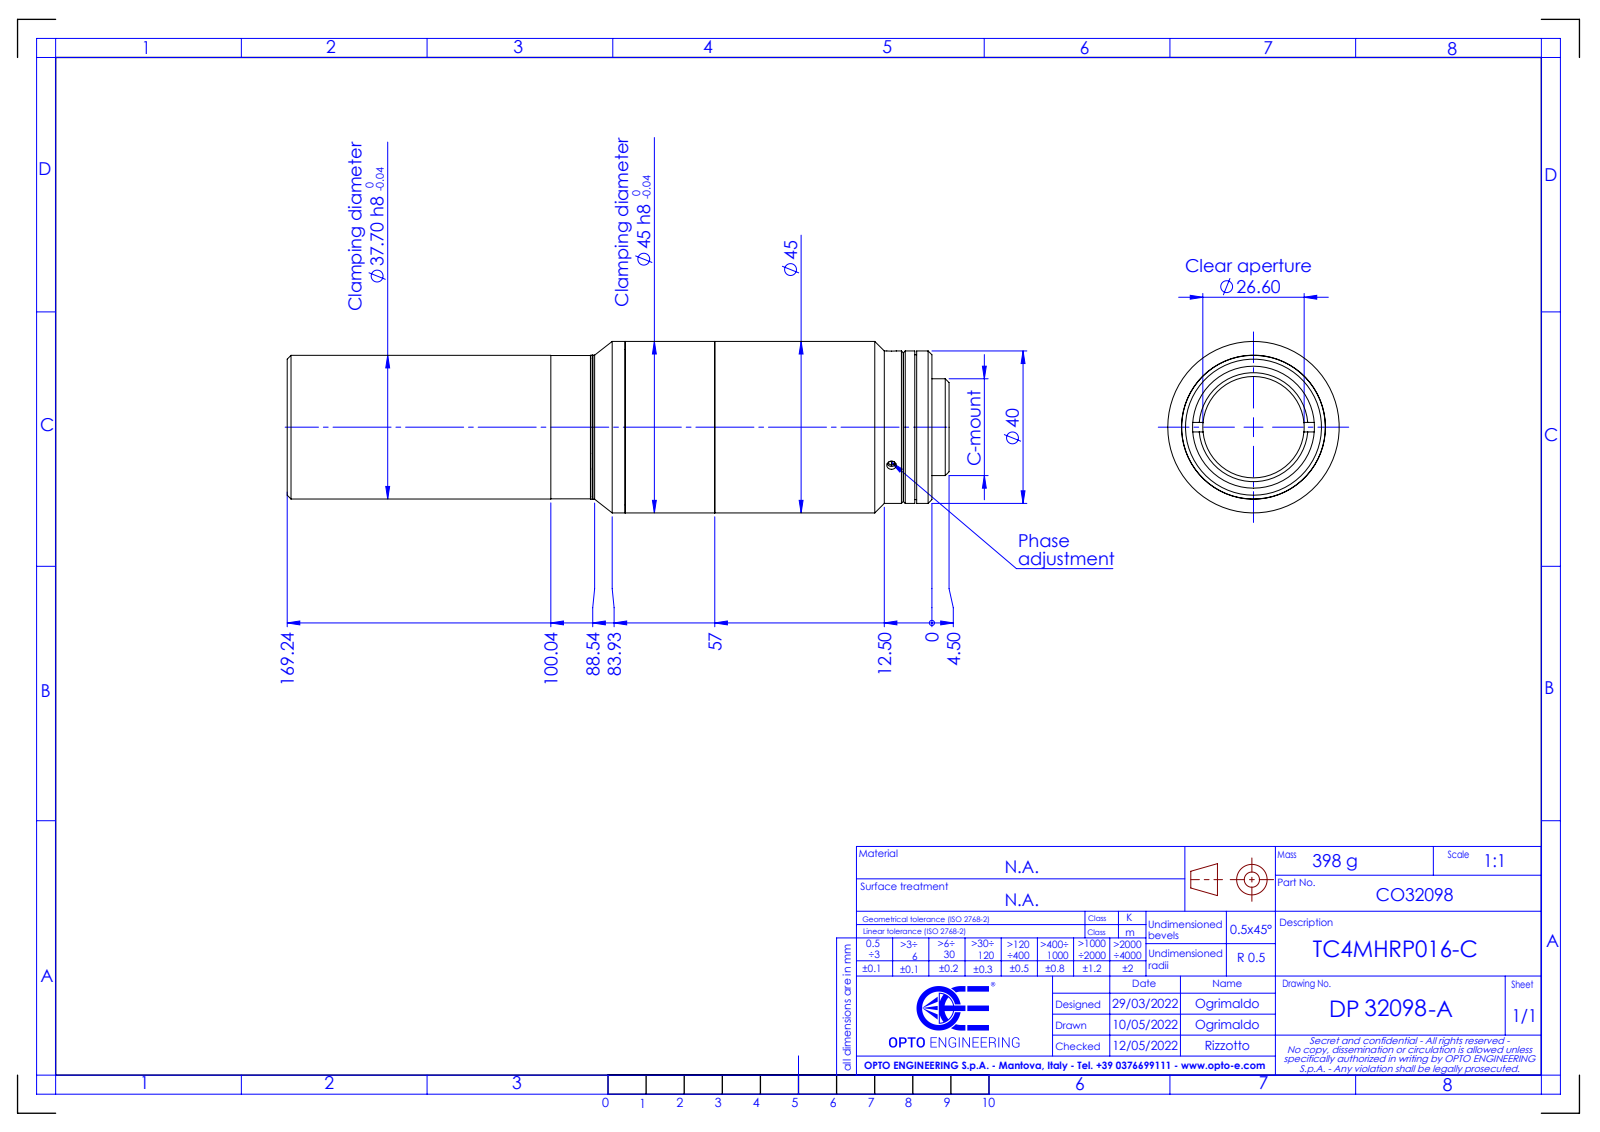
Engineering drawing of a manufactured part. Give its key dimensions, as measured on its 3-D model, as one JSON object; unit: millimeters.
{"part_name": "DP32098-A_TC4MHRP016-C", "step_written_by": "SolidWorks 2021 (CONFIG_CONTROL_DESIGN)", "units": "millimeters", "bodies": {"solids": 0, "faces": 88, "planar": 32, "cylindrical": 34, "other": 22}, "overall_size": [173.74, 45, 45], "round_holes": [[2.5, 3], [22.5, 1], [26.6, 1], [32, 1]], "round_bosses_or_shafts": [[45, 1], [40, 1], [37.8, 1], [37.7, 1], [37.6, 1], [25.4, 1]], "face_to_face_distances": [85.03, 84.54, 0.49, 89.03, 4.49, 4, 85.04, 9, 0.5, 85.53]}
